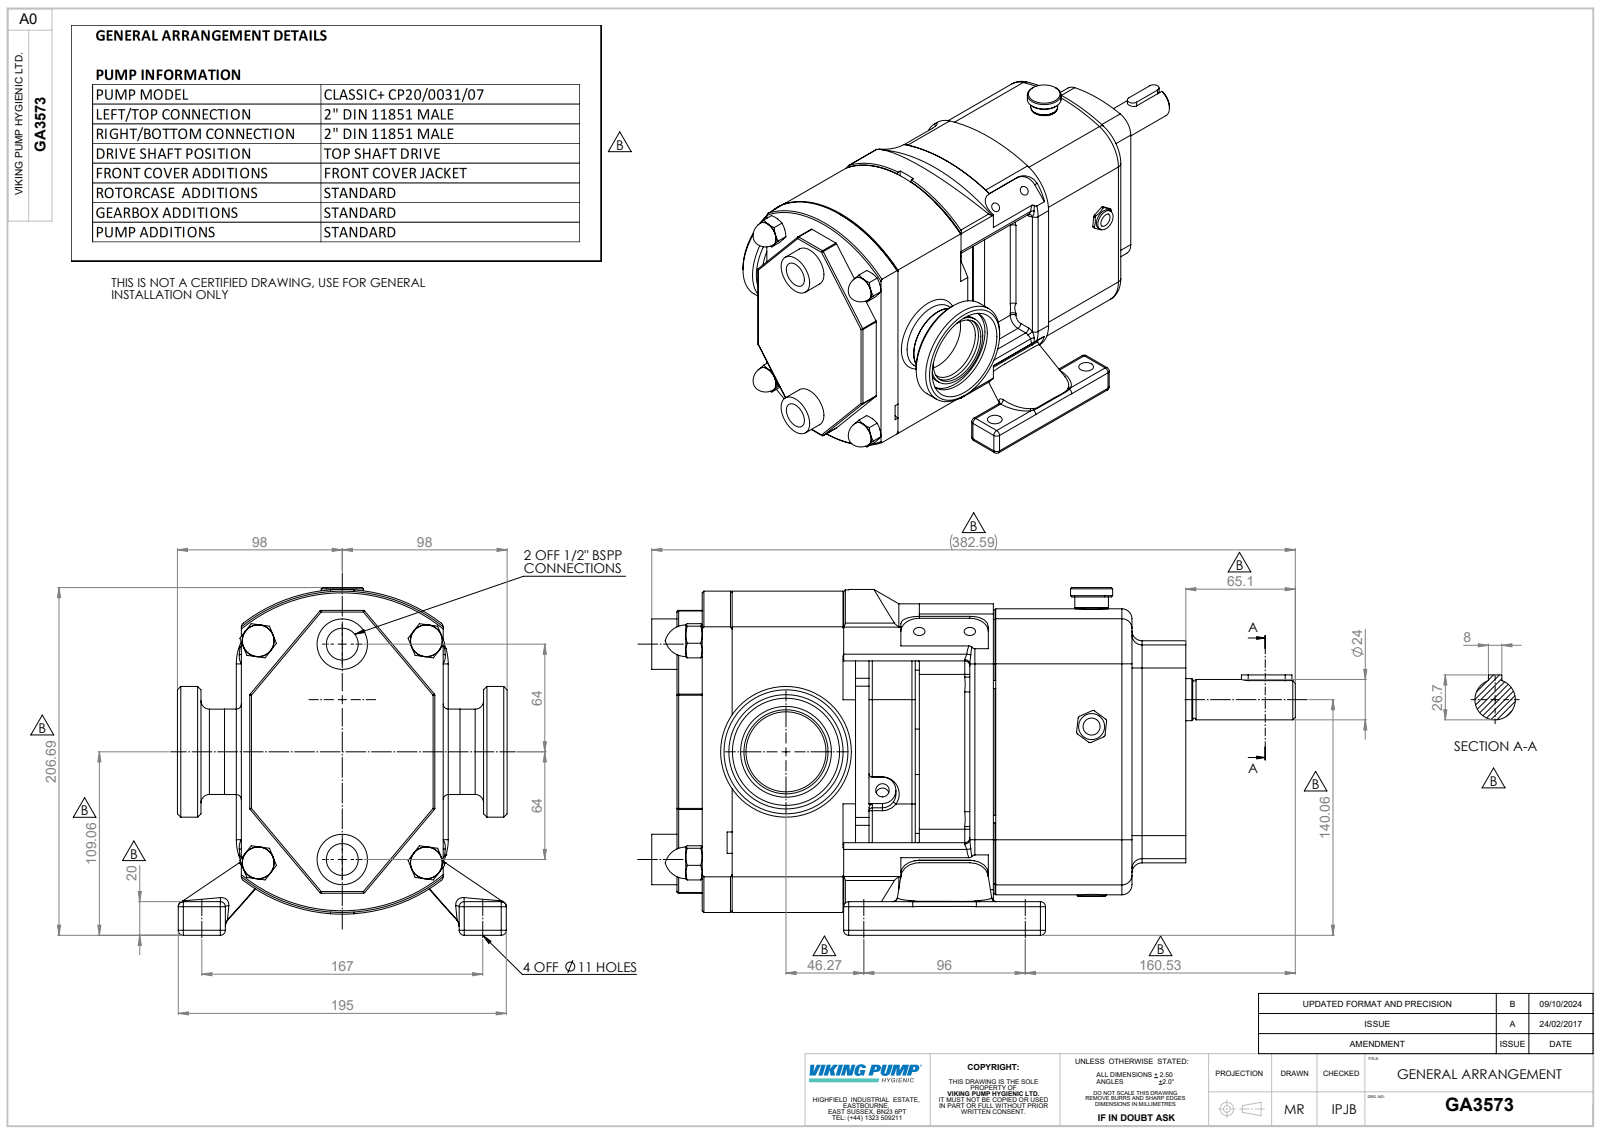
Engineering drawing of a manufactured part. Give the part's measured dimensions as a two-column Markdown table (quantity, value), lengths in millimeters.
| quantity | value |
| --- | --- |
| part name | Copy of CP20-0031-07 H T^GA3573; Copy of CP-MP20 Half Inch BSP Jacket^GA3573; GA3573; Copy of Z94-5031-33 - 2 INCH DIN11851^GA3573 |
| STEP written by | SolidWorks 2023 (AUTOMOTIVE_DESIGN) |
| units | millimeters |
| bodies | 4 solids, 893 faces (271 planar, 325 cylindrical, 297 other) |
| overall size | 382.59 × 206.69 × 196 |
| volume | 5 470 000 mm³ |
| surface area | 364 750 mm² |
| round holes (diameter × count) | 6.8 × 4, 11 × 4, 6.47 × 3, 8 × 2, 18.97 × 2, 22.53 × 1, 47.6 × 1, 50 × 1, 63.7 × 1 |
| round bosses / shafts (diameter × count) | 35 × 2, 30 × 2, 17 × 2, 77.7 × 1, 54 × 1, 50.8 × 1, 50.7 × 1, 25.02 × 1 |
| partial cylindrical surfaces (radius × count) | 3 × 55, 1 × 28, 2 × 18, 6 × 8, 11.1 × 8, 1.27 × 6, 4 × 6, 8 × 6 |
| main face-to-face distances | 120, 15, 129.09, 144.09, 158.4, 287.49, 302.49, 25, 95, 20.27 |
| hole center spacings | 53.7, 30.05, 32.05, 64, 92.35, 96, 113.72, 159.1 |
